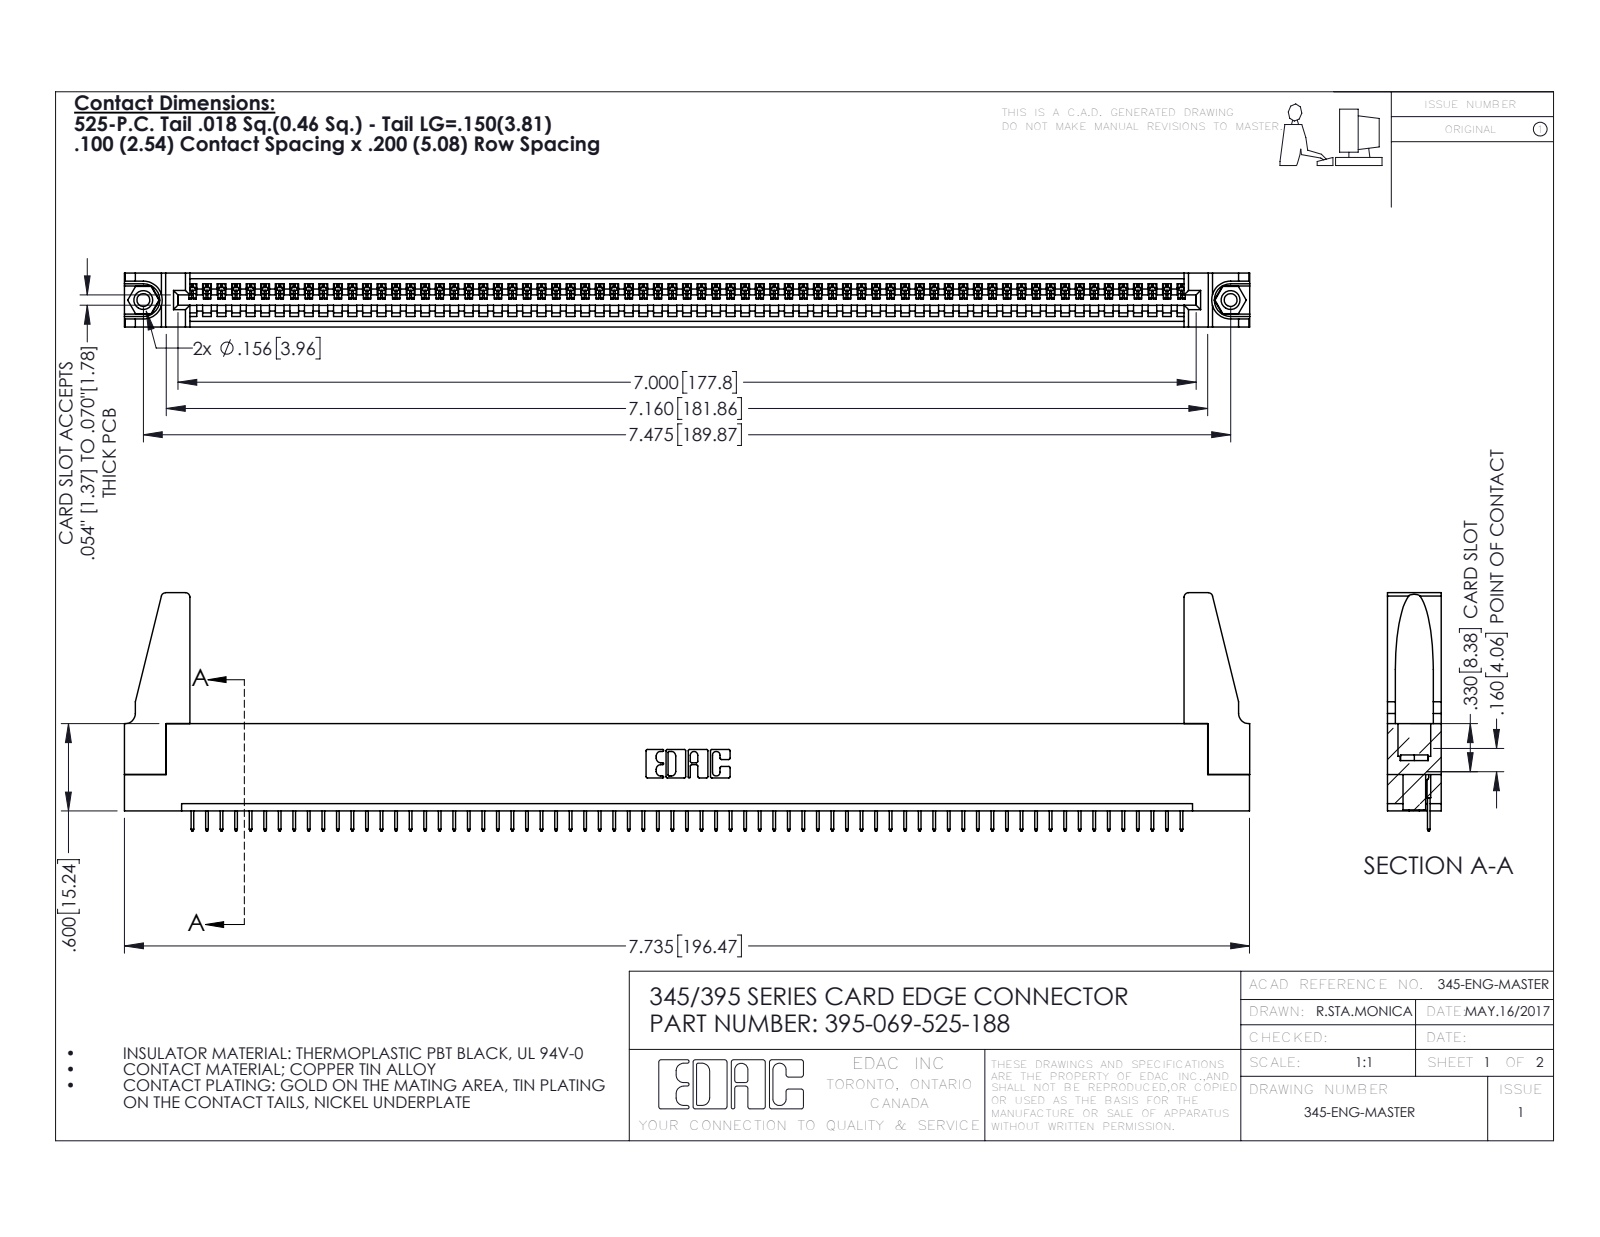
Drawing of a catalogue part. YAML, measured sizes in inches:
part_name: "345-250-001_345-250-001-102; 345-292-001_345-293-125; 395-069-525-188; 345 Part_Flush Mounting Lugs - 0.156 Dia-TH (+1 more)"
step_written_by: "SolidWorks 2020 (CONFIG_CONTROL_DESIGN)"
units: inches
bodies: {solids: 74, faces: 4528, planar: 3326, cylindrical: 1186, other: 16}
overall_size: [7.736, 1.637, 0.37]
volume: 1.334
surface_area: 42.28
round_holes:
  - {diameter: 0.089, count: 2}
  - {diameter: 0.125, count: 2}
  - {diameter: 0.156, count: 2}
  - {diameter: 0.064, count: 1}
round_bosses_or_shafts:
  - {diameter: 0.155, count: 2}
partial_cylinders:
  - {radius: 0.006, count: 138}
  - {radius: 0.01, count: 22}
  - {radius: 0.03, count: 8}
  - {radius: 0.007, count: 6}
  - {radius: 0.031, count: 6}
  - {radius: 0.026, count: 3}
  - {radius: 0.031, count: 2}
  - {radius: 0.04, count: 2}
face_to_face_distances: [0.072, 0.298, 0.37, 0.2, 0.098, 0.272, 0.025, 0.225, 0.072, 0.149]
hole_center_spacings: [0.27, 7.239, 7.475]
